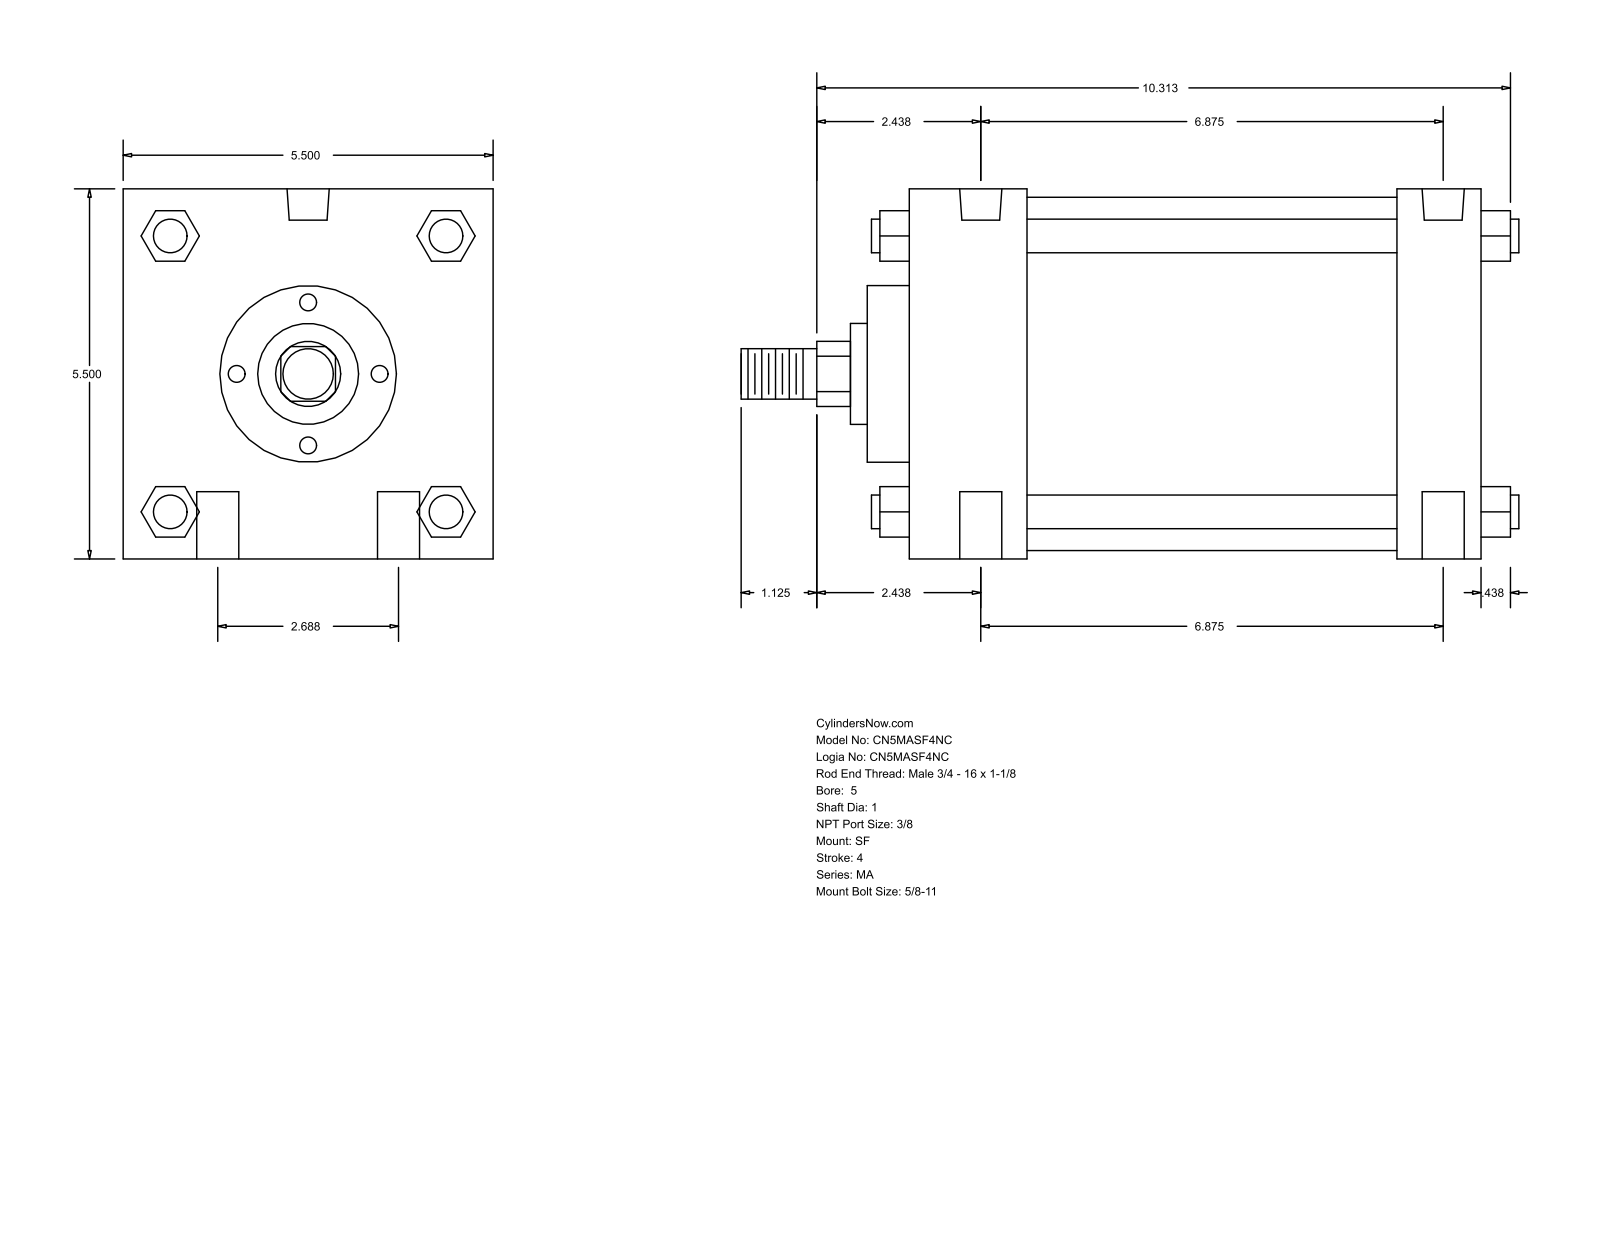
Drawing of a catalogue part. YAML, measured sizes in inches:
part_name: "MA_SF__0500_1"
step_written_by: "GSSL Pune (CONFIG_CONTROL_DESIGN)"
units: inches
bodies: {solids: 0, faces: 126, planar: 95, cylindrical: 31, other: 0}
overall_size: [11.563, 5.5, 5.5]
round_holes:
  - {diameter: 0.625, count: 4}
  - {diameter: 0.437, count: 2}
  - {diameter: 0.627, count: 2}
round_bosses_or_shafts:
  - {diameter: 0.5, count: 4}
  - {diameter: 5.25, count: 1}
  - {diameter: 2.625, count: 1}
  - {diameter: 1.5, count: 1}
  - {diameter: 1, count: 1}
  - {diameter: 0.75, count: 1}
partial_cylinders:
  - {radius: 0.484, count: 1}
face_to_face_distances: [5.5, 8.5, 1.75, 7.25, 5.5, 6.75, 1.25, 0.625, 2.375, 7.875]
hole_center_spacings: [1.344, 7.005, 6.875, 2.687, 7.382, 6.5]
